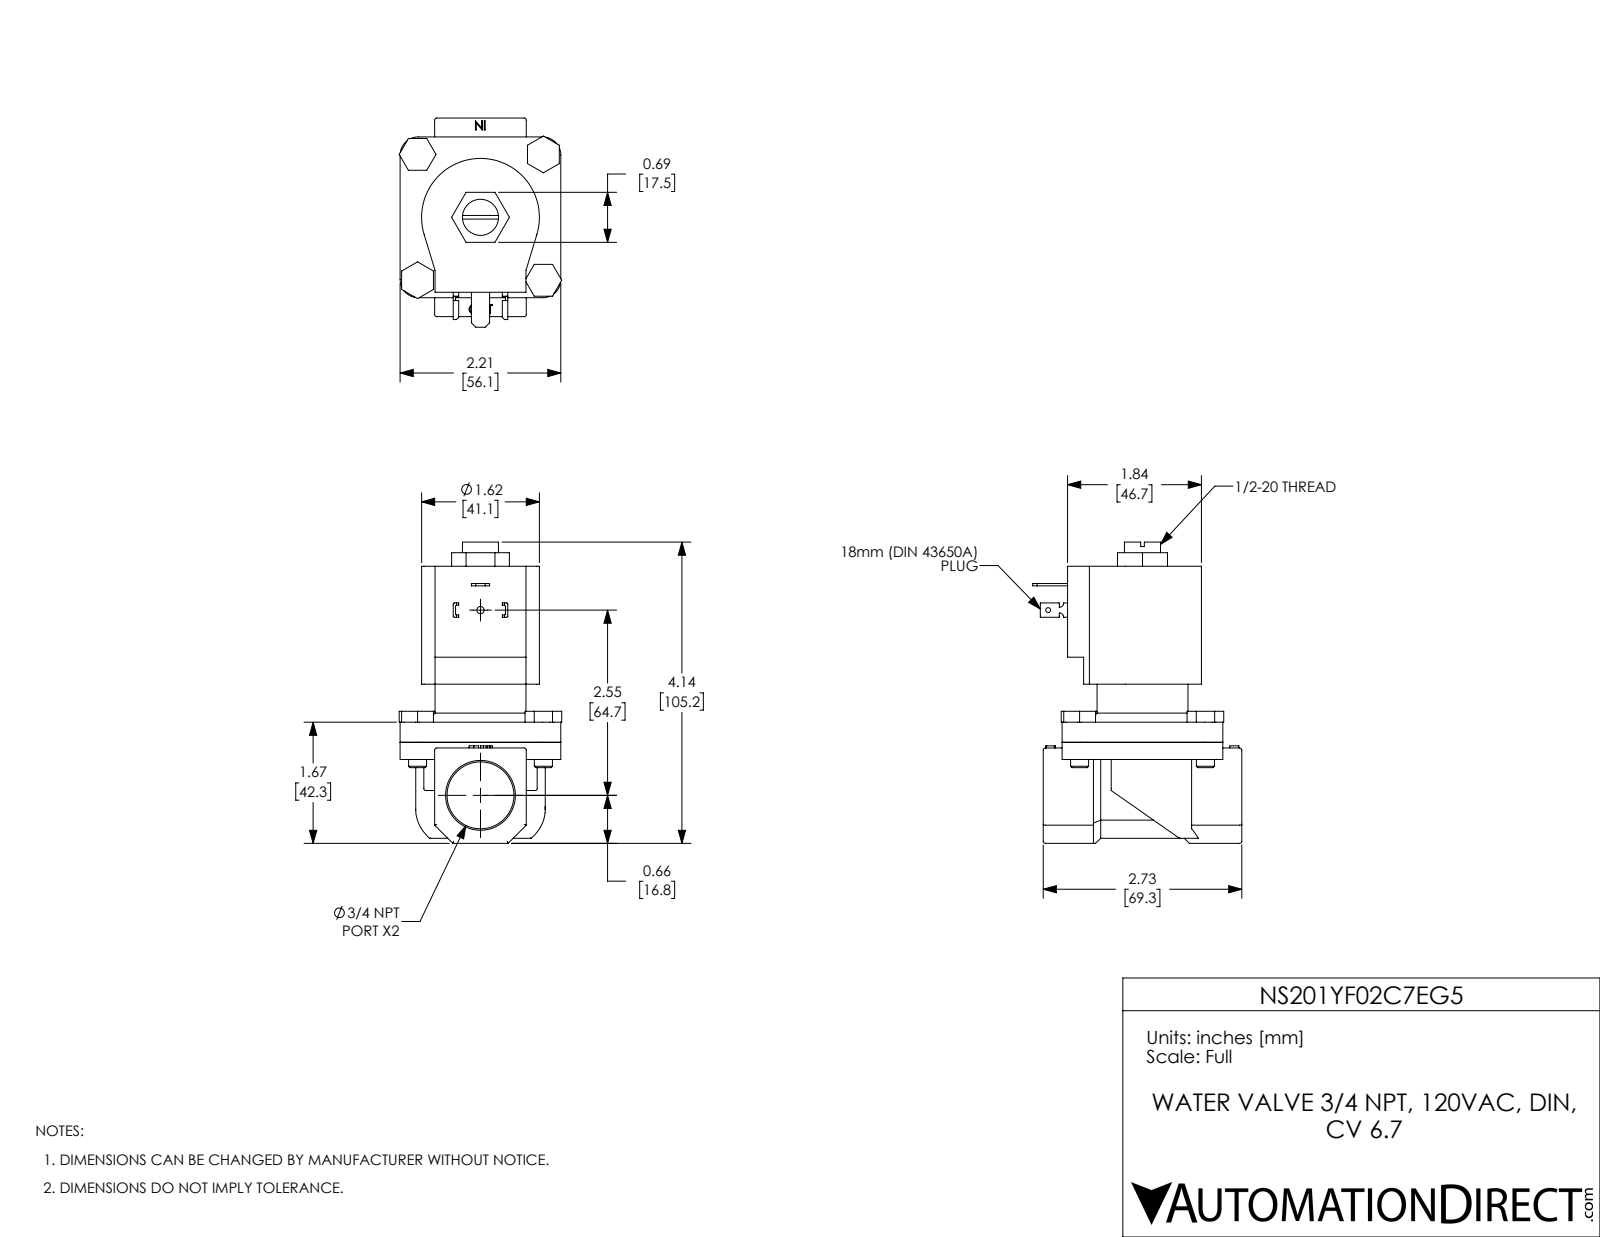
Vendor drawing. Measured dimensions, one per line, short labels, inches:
name: NS201YF02C7EG5
written by: SolidWorks 2021 (CONFIG_CONTROL_DESIGN)
unit: in
bodies: 11 solids, 332 faces (198 planar, 99 cylindrical, 35 other)
size: 4.14 × 2.875 × 2.235
volume: 10.32 in³; area: 67.12 in²
holes: 4× ⌀0.25, 1× ⌀0.067, 1× ⌀0.1, 1× ⌀0.496, 1× ⌀0.512, 1× ⌀0.92, 1× ⌀1.155
bosses: 4× ⌀0.248, 1× ⌀1.25
rounds: 15× R0.03, 8× R0.015, 4× R0.25, 2× R0.06, 1× R0.81, 1× R0.89
face distances: 0.276, 2.419, 2.143, 0.475, 1.735, 2.21, 0.236, 0.512, 2.655, 0.26
hole spacings: 1.223, 1.73, 2.446, 2.546
